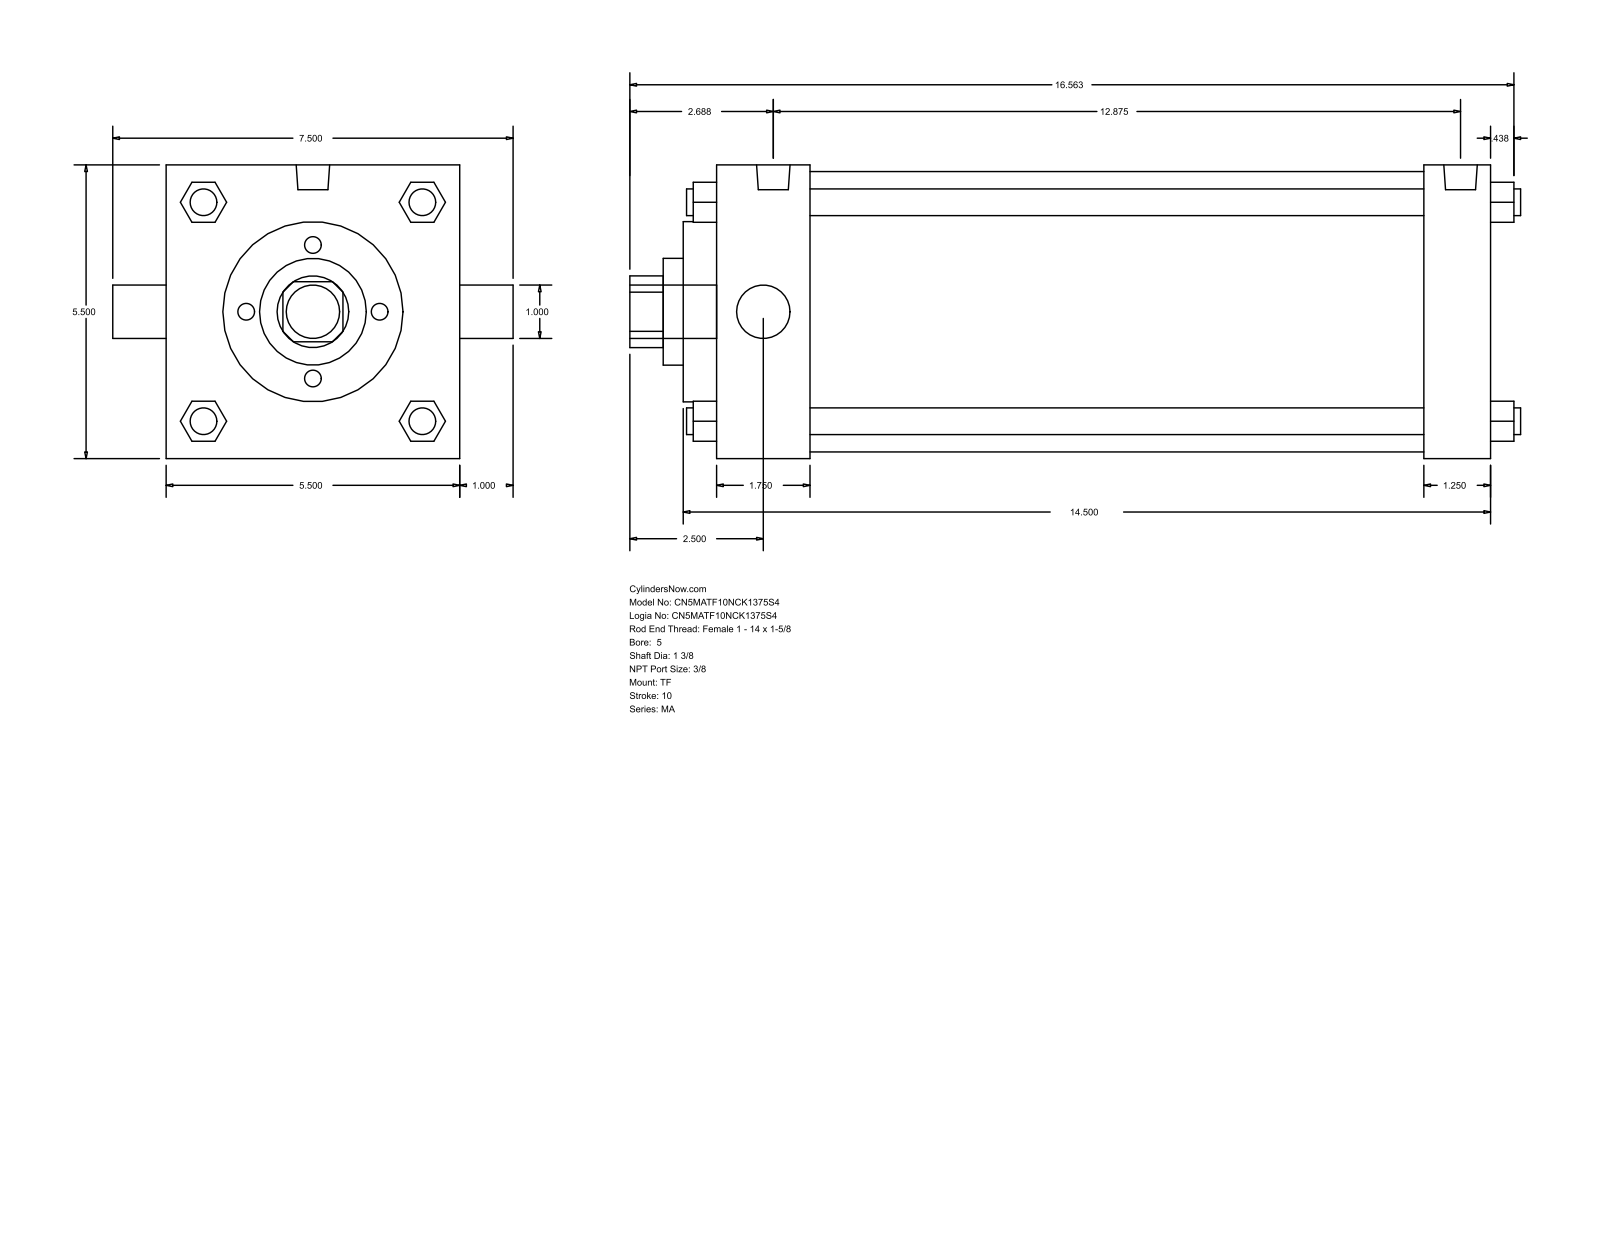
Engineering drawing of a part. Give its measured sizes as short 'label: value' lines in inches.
name: MA_TF__0500_1.375
written by: GSSL Pune (CONFIG_CONTROL_DESIGN)
unit: in
bodies: 0 solids, 122 faces (93 planar, 29 cylindrical, 0 other)
size: 16.687 × 7.5 × 5.5
holes: 1× ⌀1, 1× ⌀1.375, 1× ⌀2, 1× ⌀3.375, 1× ⌀5.25
bosses: 4× ⌀0.5, 3× ⌀0.437, 2× ⌀0.627, 1× ⌀1
rounds: 1× R0.672
face distances: 5.5, 14.5, 13.25, 1.25, 1.75, 11.5, 12.75, 0.625, 2.375, 13.875
